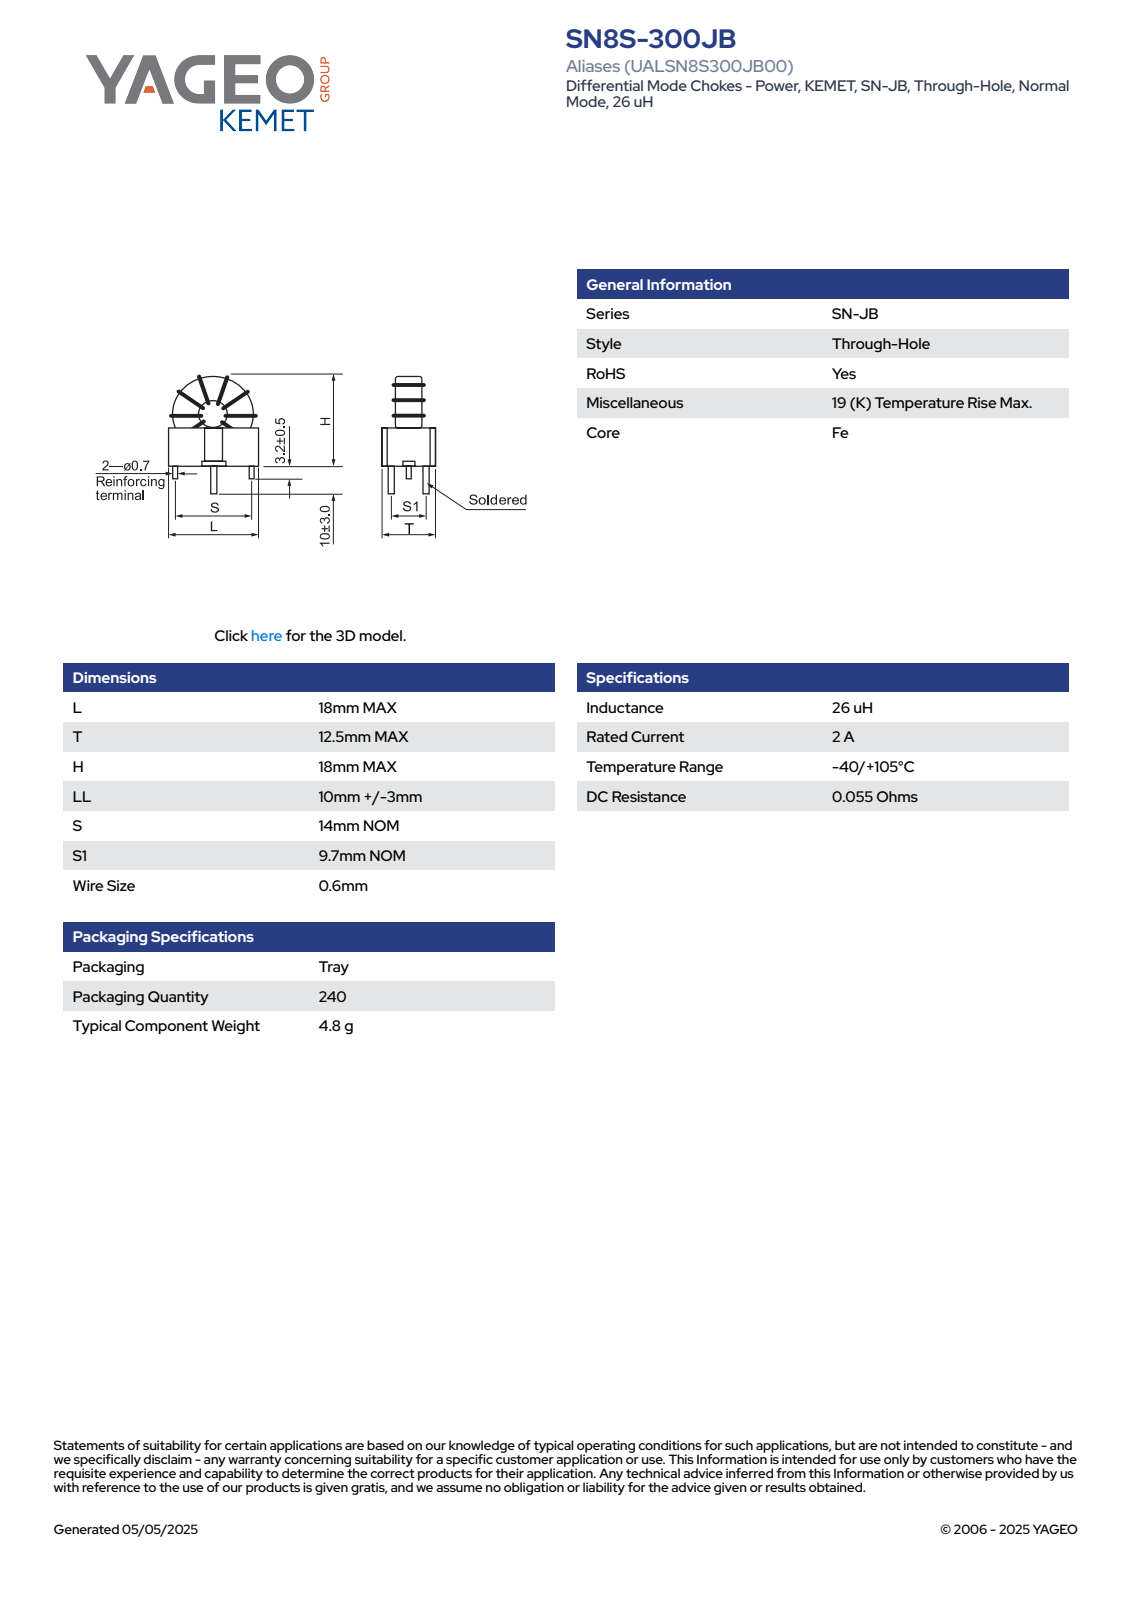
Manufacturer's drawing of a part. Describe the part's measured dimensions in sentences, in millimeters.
The part is named "SN8S-300JB". Its 3-D file was written by "SolidWorks 2018 (AUTOMOTIVE_DESIGN)". It is 1 solid with 153 faces: 94 planar, 47 cylindrical and 12 other. Overall it measures 28 by 18 by 12.5 millimeters. Its volume is 2 267 cubic millimeters and its surface area 2 047 square millimeters. Round holes: 2 of diameter 0.7, 1 of diameter 6.5. Round bosses or shafts: 2 of diameter 0.7, 2 of diameter 0.6, 1 of diameter 15.8. Partial cylindrical surfaces (rounded edges, fillets, slot ends): 4 of radius 0.1, 4 of radius 0.2, 4 of radius 1, 4 of radius 2.25, 2 of radius 0.5, 1 of radius 0.3, 1 of radius 7.91, 1 of radius 8. The main face-to-face distances are 0.55, 8.85, 0.5, 8.9, 8.35, 9.4, 8.3, 18, 8.4, 9.1. The hole center spacings are 9.7.
